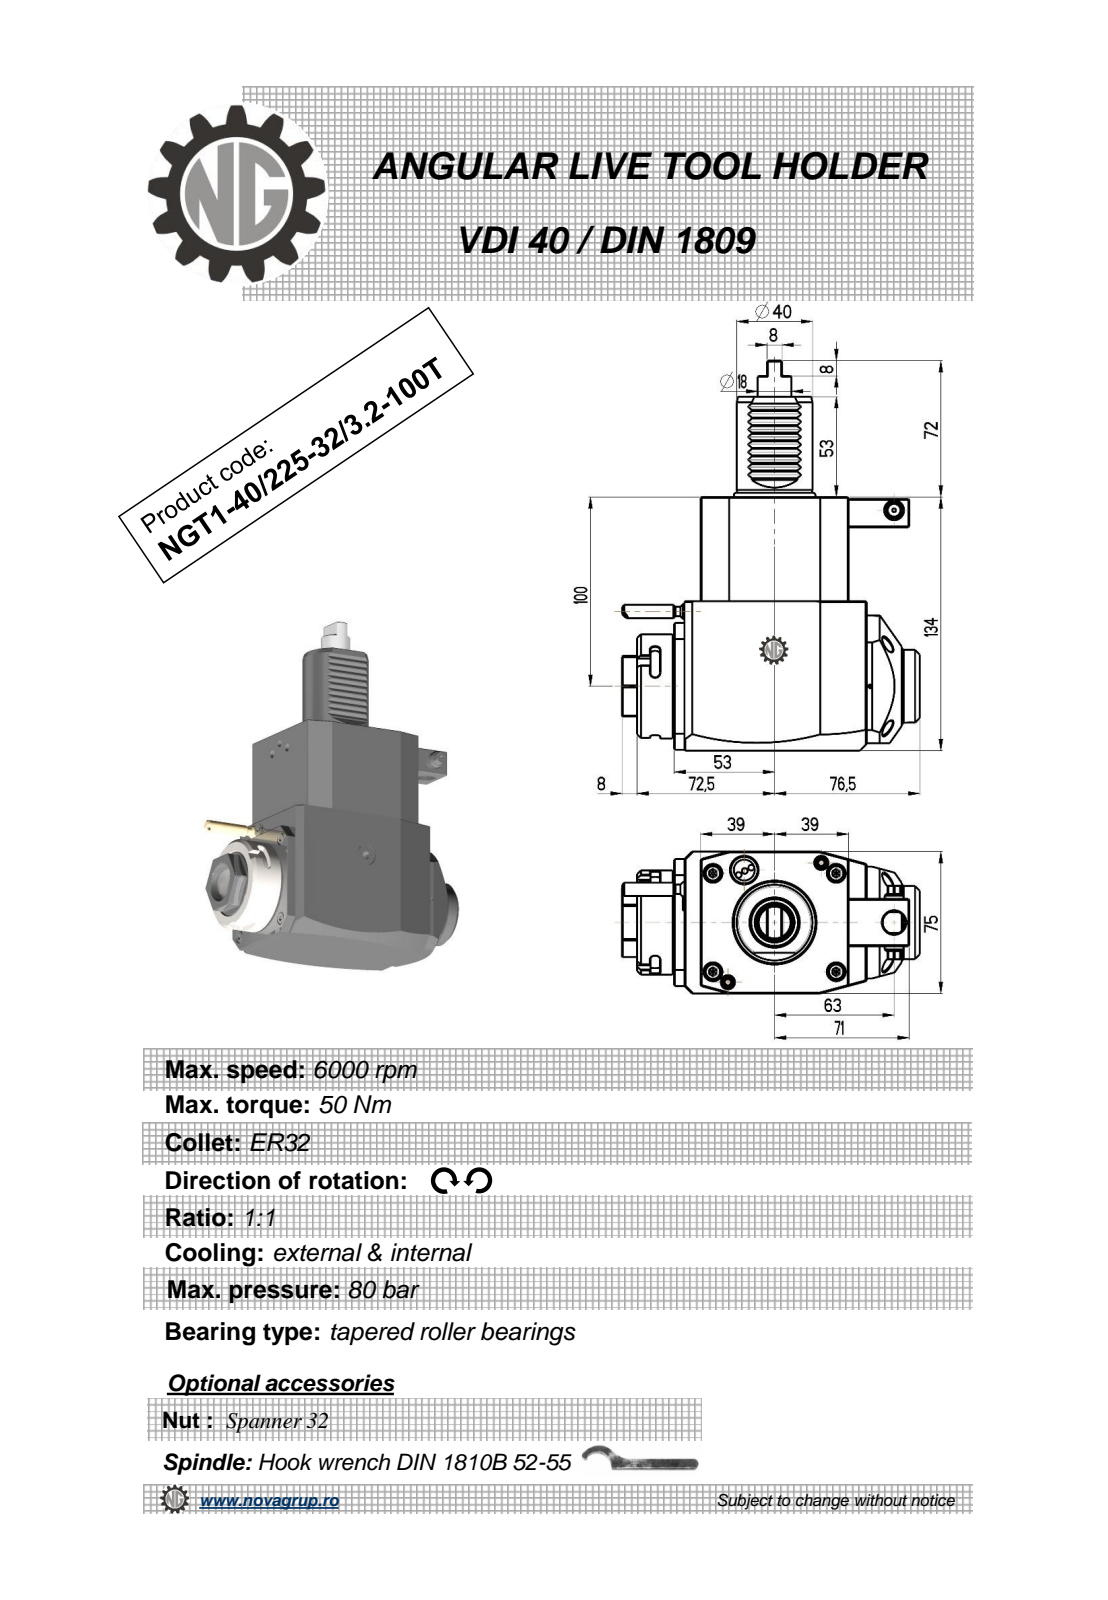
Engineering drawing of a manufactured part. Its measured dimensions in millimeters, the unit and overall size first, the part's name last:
Units: millimetres
Overall size (bounding box): 206 × 157 × 75
Round holes (diameter × count): ⌀2 ×1, ⌀2.5 ×1, ⌀3 ×1, ⌀4.5 ×1, ⌀9.5 ×1, ⌀12 ×1, ⌀23 ×1
Round bosses / shafts (diameter × count): ⌀8 ×2, ⌀55 ×1, ⌀48 ×1, ⌀40 ×1, ⌀38.5 ×1, ⌀17.8 ×1, ⌀10 ×1, ⌀7 ×1
Partial cylindrical surfaces — rounded edges, fillets, slot ends (radius × count): R0.3 ×10, R2.5 ×6, R0.8 ×2, R180 ×2, R0.5 ×1, R3.85 ×1, R4.25 ×1, R24.5 ×1
Main face-to-face distances: 75, 134, 78, 14, 92, 25, 84.88, 19.5, 33.5, 111.5
Hole centre spacings: 43.2, 55.81, 92.5
Volume: 1 081 000 mm³ · Surface area: 78 187 mm²
Bodies: 1 solid, 351 faces (189 planar, 86 cylindrical, 76 other)
Part name (STEP PRODUCT): NGT1_40_225_32_3_2_100T
STEP written by: PRO/ENGINEER BY PARAMETRIC TECHNOLOGY CORPORATION, 2010280 (CONFIG_CONTROL_DESIGN)
